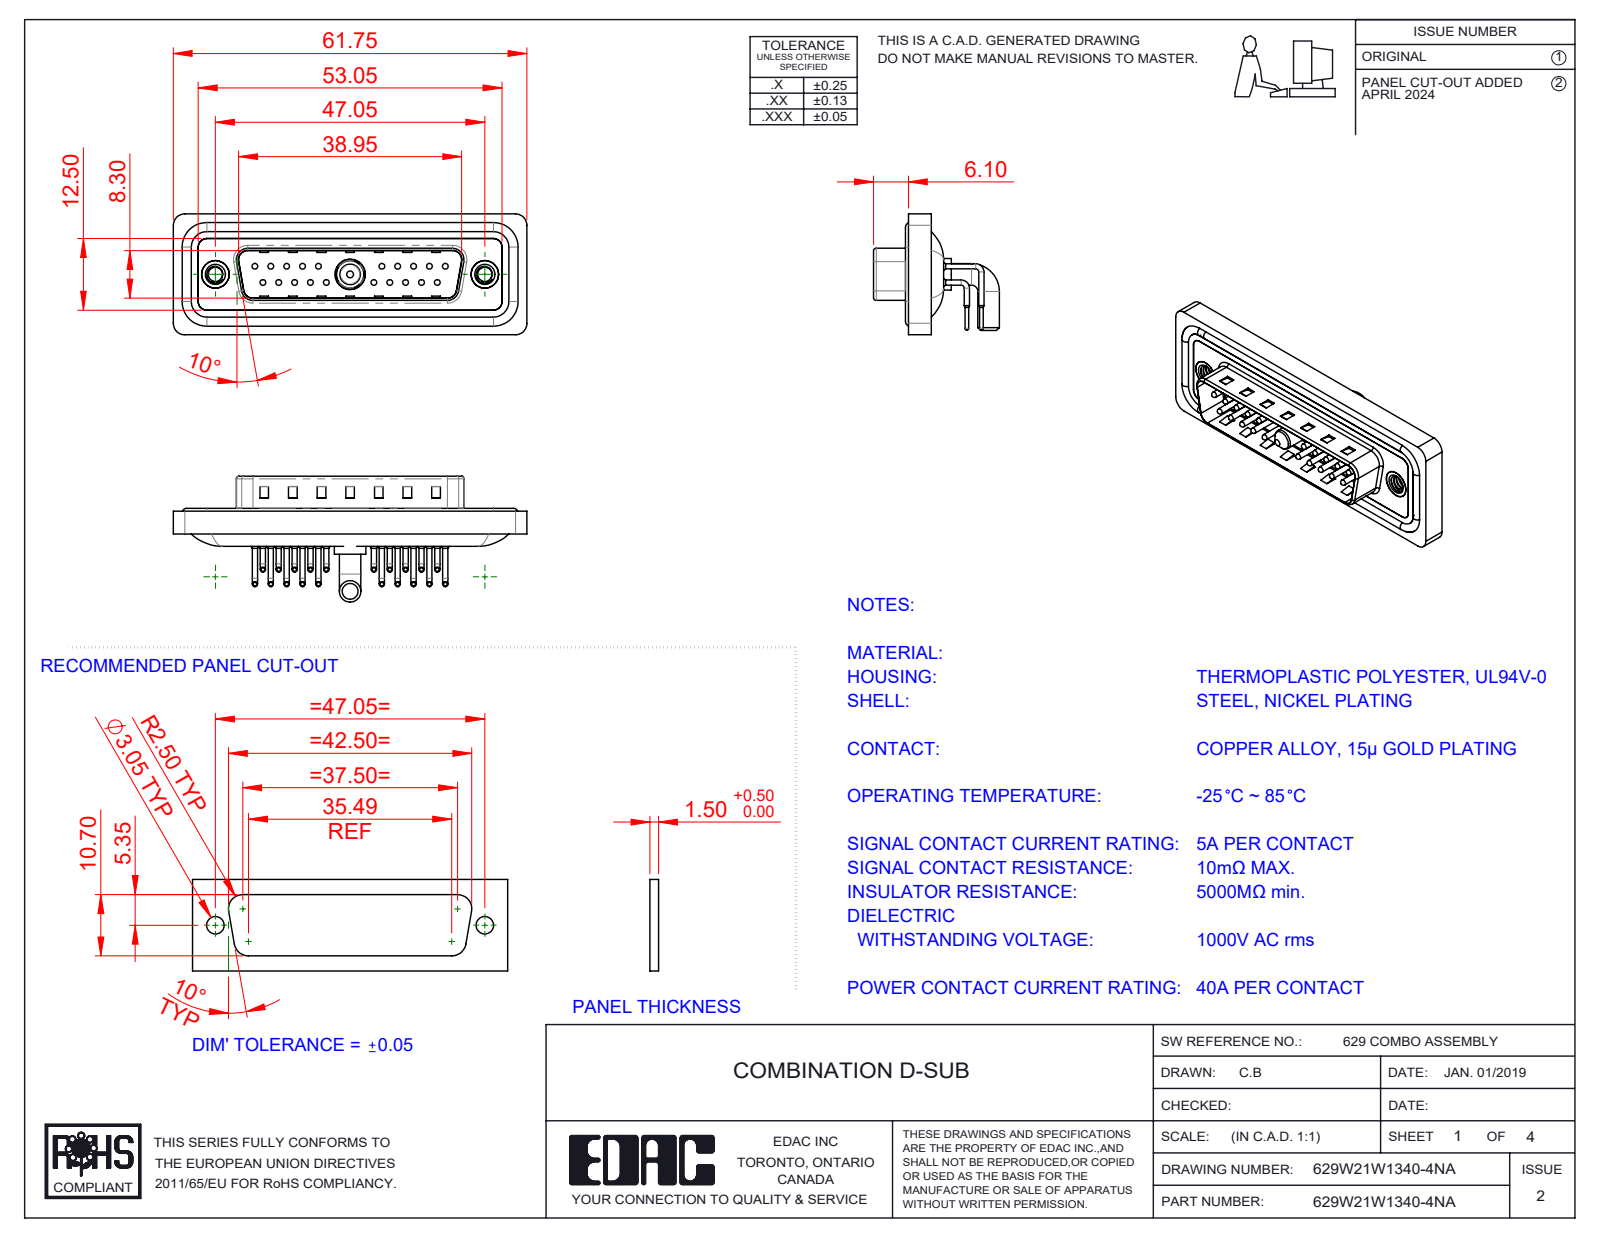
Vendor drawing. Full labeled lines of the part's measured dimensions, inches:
Part name (STEP PRODUCT): 629Combo Waterproof Housing_25 Contacts; 629Combo Shell Rear_25 Contacts; 629Combo Housing_21W1; 629Combo Contact Row 2 (+5 more)
STEP written by: SolidWorks 2023 (CONFIG_CONTROL_DESIGN)
Units: inches
Bodies: 29 solids, 2720 faces (1499 planar, 927 cylindrical, 294 other)
Overall size (bounding box): 2.431 × 0.865 × 0.831
Volume: 0.457 in³ · Surface area: 19.79 in²
Round holes (diameter × count): ⌀0.03 ×20, ⌀0.063 ×20, ⌀0.079 ×20, ⌀0.098 ×2, ⌀0.157 ×2, ⌀0.189 ×2, ⌀0.197 ×2, ⌀0.191 ×1, ⌀0.209 ×1
Round bosses / shafts (diameter × count): ⌀0.035 ×40, ⌀0.059 ×20, ⌀0.039 ×20, ⌀0.026 ×20, ⌀0.063 ×4, ⌀0.193 ×2, ⌀0.148 ×2, ⌀0.217 ×1
Partial cylindrical surfaces — rounded edges, fillets, slot ends (radius × count): R0.04 ×20, R0.059 ×18, R0.079 ×18, R0.02 ×8, R0.063 ×8, R0.01 ×4, R0.024 ×4, R0.026 ×4
Main face-to-face distances: 0.016, 0.114, 0.031, 0.161, 0.043, 0.083, 0.063, 0.177, 0.059, 0.098
Hole centre spacings: 0.124, 0.109, 0.218, 0.327, 0.198, 0.763, 0.826, 0.872
